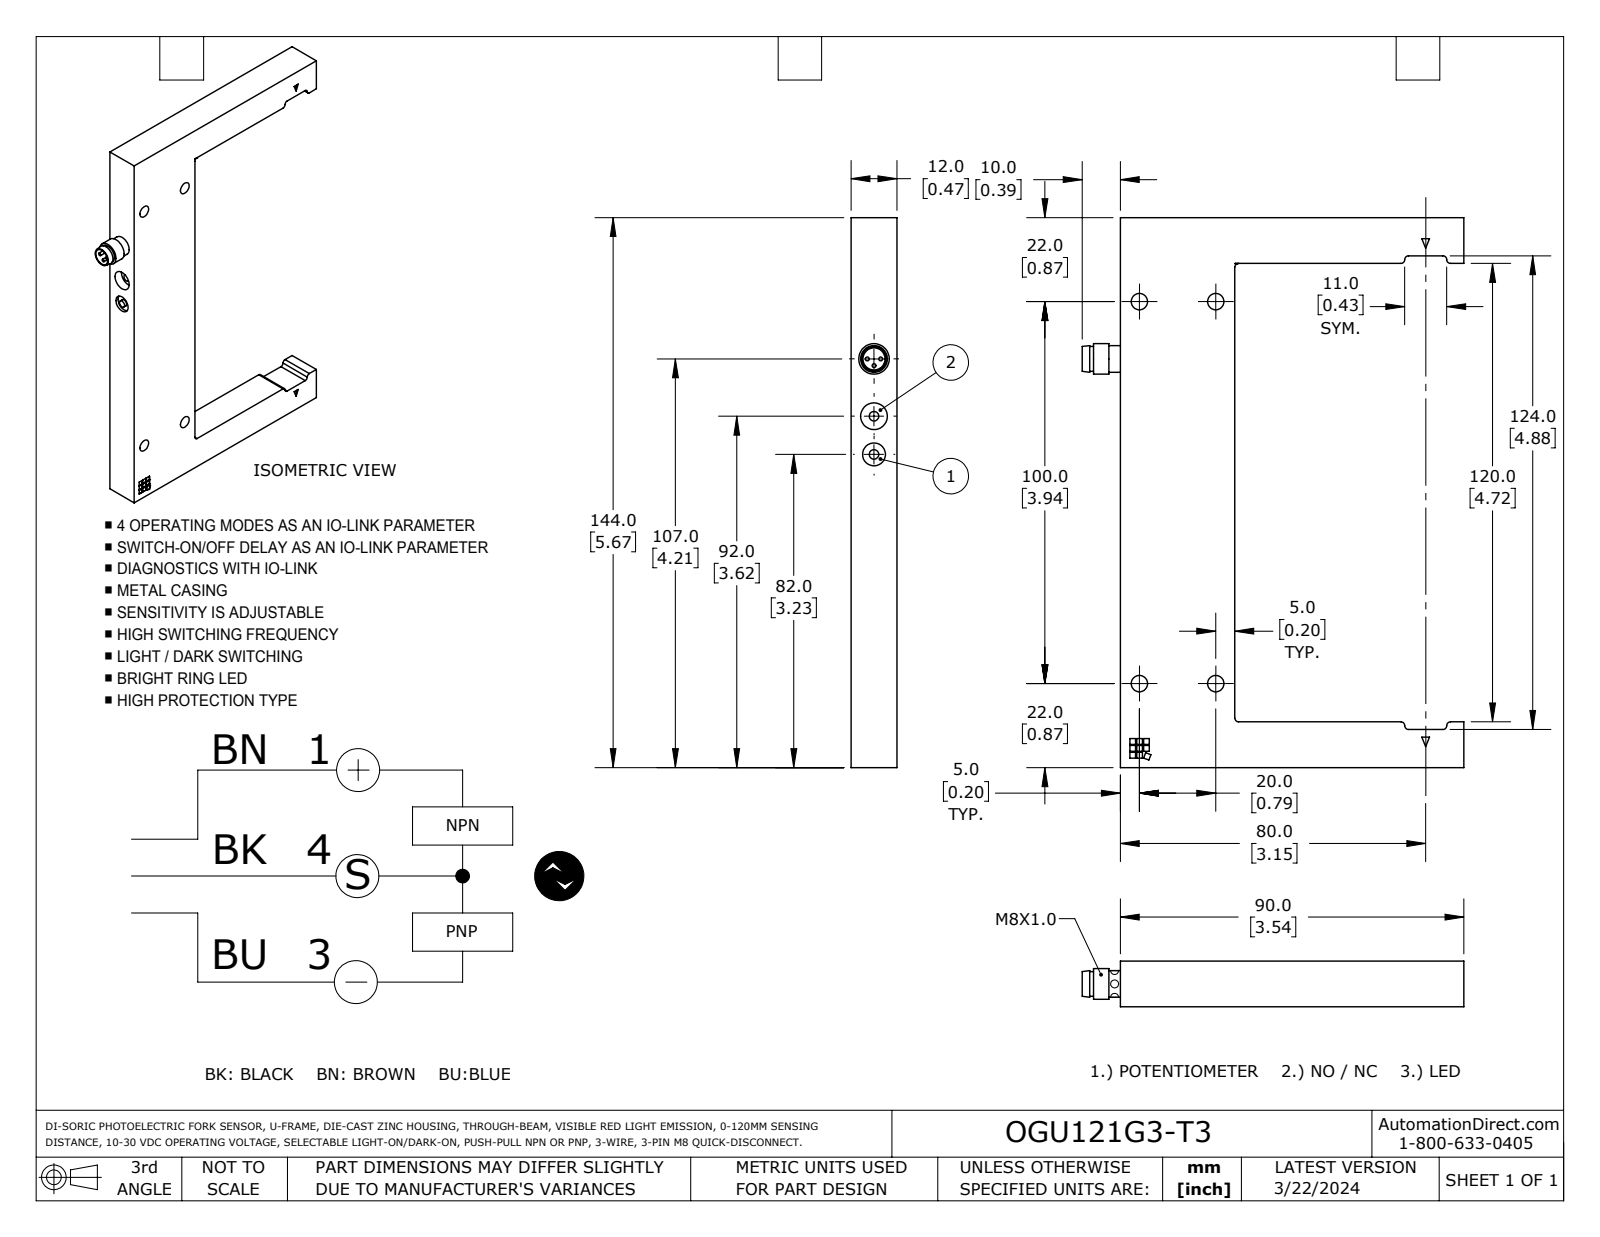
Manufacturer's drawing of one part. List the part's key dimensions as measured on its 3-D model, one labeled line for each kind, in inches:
Part name (STEP PRODUCT): OGU121G3-T3
STEP written by: SolidWorks 2023 (AUTOMOTIVE_DESIGN)
Units: inches
Bodies: 1 solid, 121 faces (93 planar, 27 cylindrical, 1 other)
Overall size (bounding box): 5.669 × 3.937 × 0.472
Volume: 4.152 in³ · Surface area: 30.39 in²
Round holes (diameter × count): ⌀0.169 ×4, ⌀0.118 ×1, ⌀0.228 ×1, ⌀0.236 ×1, ⌀0.276 ×1
Round bosses / shafts (diameter × count): ⌀0.039 ×3, ⌀0.098 ×2, ⌀0.315 ×1, ⌀0.276 ×1, ⌀0.256 ×1
Partial cylindrical surfaces — rounded edges, fillets, slot ends (radius × count): R0.039 ×11
Main face-to-face distances: 0.472, 1.181, 5.197, 5.669, 4.724, 3.543, 2.362, 0.079, 0.394, 5.276
Hole centre spacings: 0.787, 3.937, 4.015, 0.394, 0.591, 0.984
